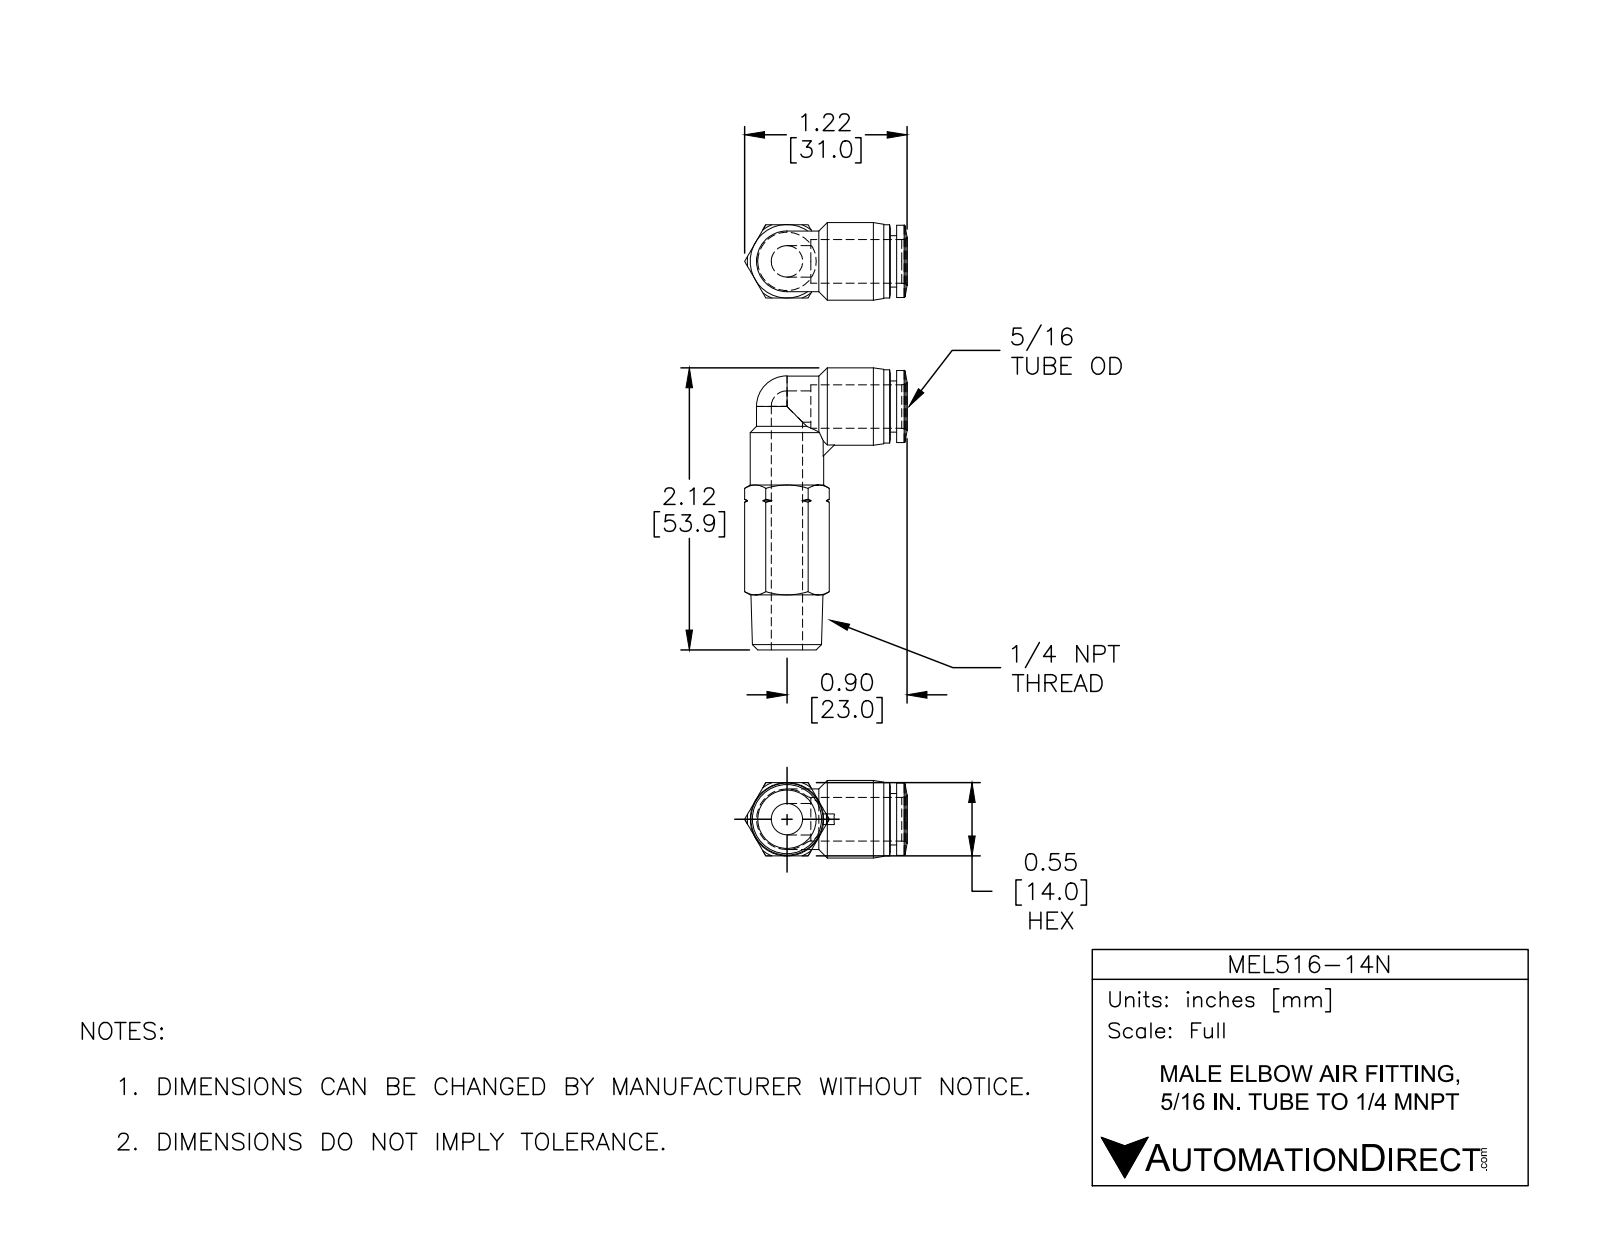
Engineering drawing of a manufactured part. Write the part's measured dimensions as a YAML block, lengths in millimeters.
part_name: "MEL516-14N"
step_written_by: "SolidWorks 2015 (CONFIG_CONTROL_DESIGN)"
units: millimeters
bodies: {solids: 1, faces: 87, planar: 15, cylindrical: 21, other: 51}
overall_size: [53.9, 31, 14.8]
volume: 7900
surface_area: 4845
round_holes:
  - {diameter: 6, count: 2}
  - {diameter: 8.3, count: 1}
round_bosses_or_shafts:
  - {diameter: 14, count: 2}
  - {diameter: 14.8, count: 1}
  - {diameter: 13.8, count: 1}
  - {diameter: 11.6, count: 1}
  - {diameter: 9.8, count: 1}
partial_cylinders:
  - {radius: 5.8, count: 1}
face_to_face_distances: [14, 1.2, 15.2, 16.4, 6, 8, 13.9, 1.2, 2.4, 10.5]
